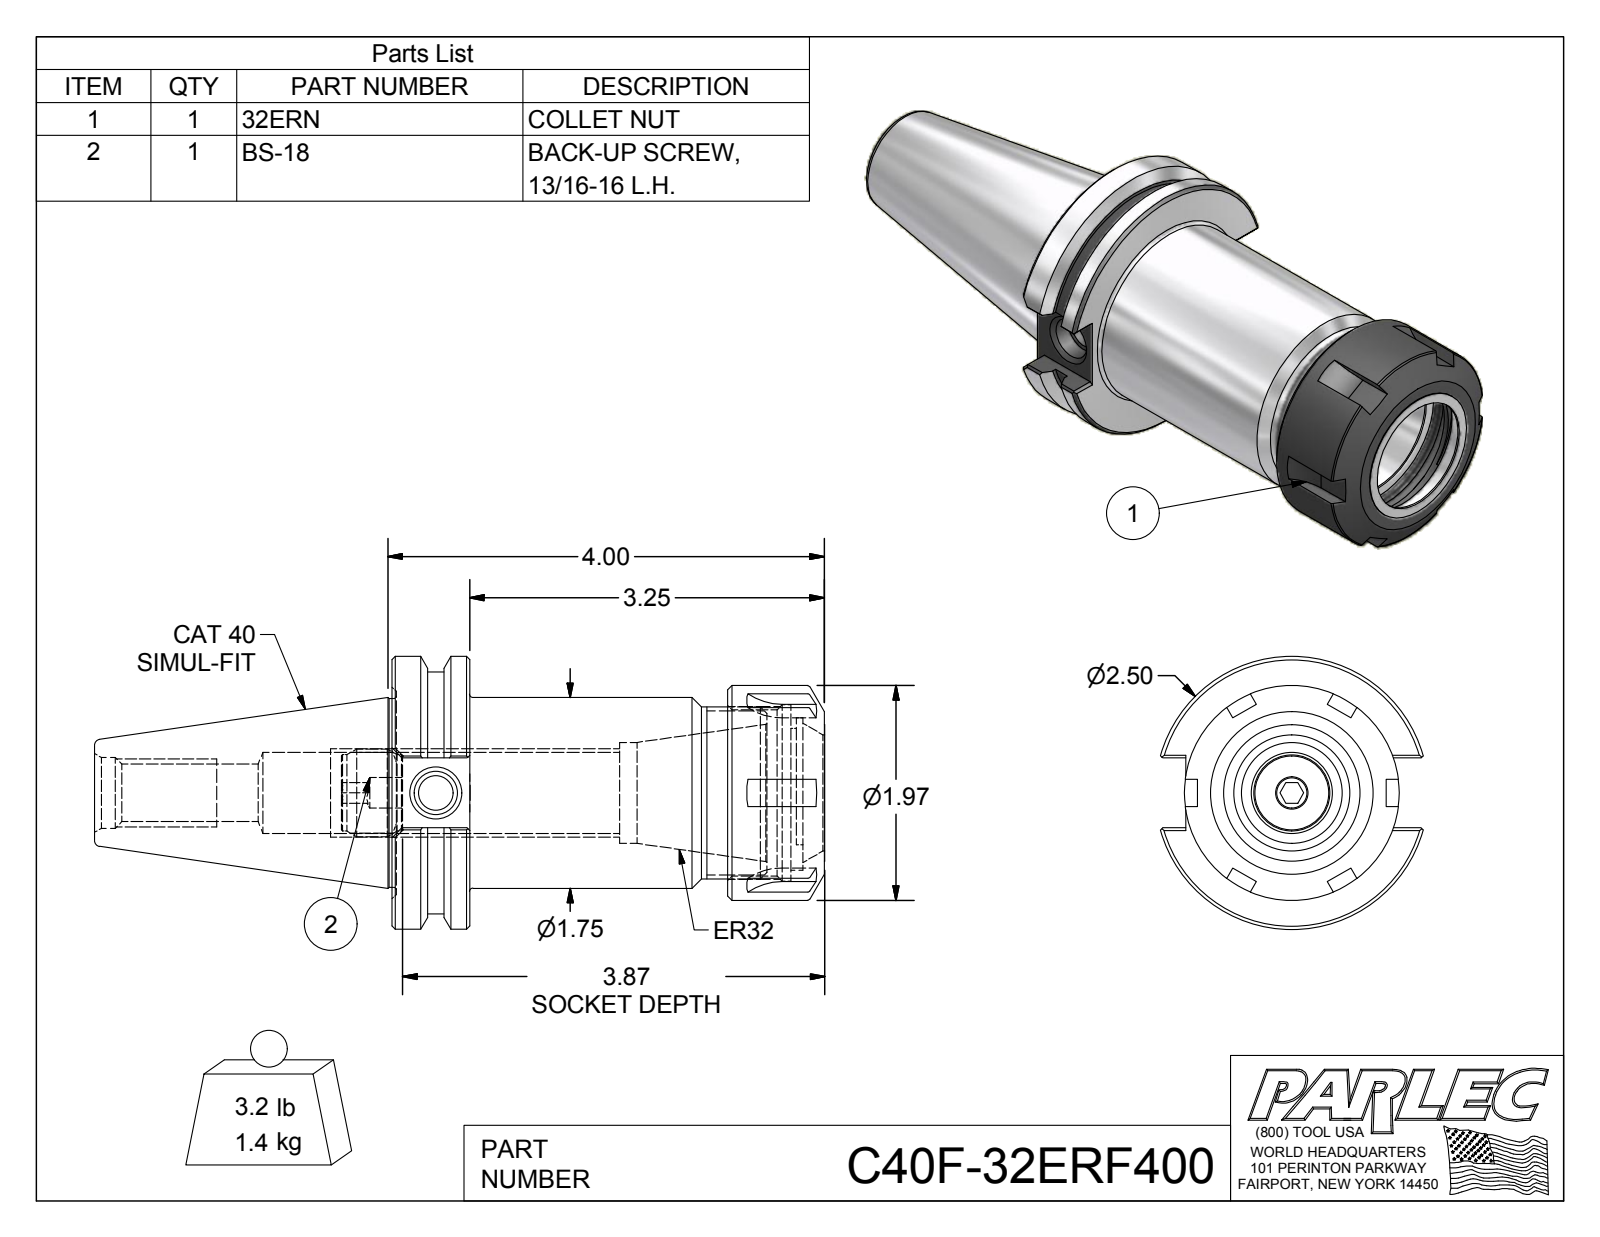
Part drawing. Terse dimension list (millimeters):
name: C40F-32ER4-1; 32ERN; BS-18; C40F-32ERF400
written by: Autodesk Inventor 2016 (AUTOMOTIVE_DESIGN)
unit: mm
bodies: 3 solids, 175 faces (75 planar, 37 cylindrical, 63 other)
size: 169.86 × 63.5 × 61.11
volume: 190 696 mm³; area: 45 588 mm²
holes: 1× ⌀7.11, 1× ⌀8, 1× ⌀10.13, 1× ⌀13.39, 1× ⌀16.46, 1× ⌀18.92, 1× ⌀23.5, 1× ⌀27, 1× ⌀33.02, 1× ⌀38.65, 1× ⌀41
bosses: 1× ⌀63.5, 1× ⌀56.26, 1× ⌀50, 1× ⌀44.45, 1× ⌀40, 1× ⌀20.45, 1× ⌀17.78
rounds: 12× R0.51, 1× R14.9, 1× R17.5
face distances: 18.04, 77.81, 100.59, 82.55, 59.77, 22.78, 92.82, 74.78, 15.01, 7.77
hole spacings: 1.85
